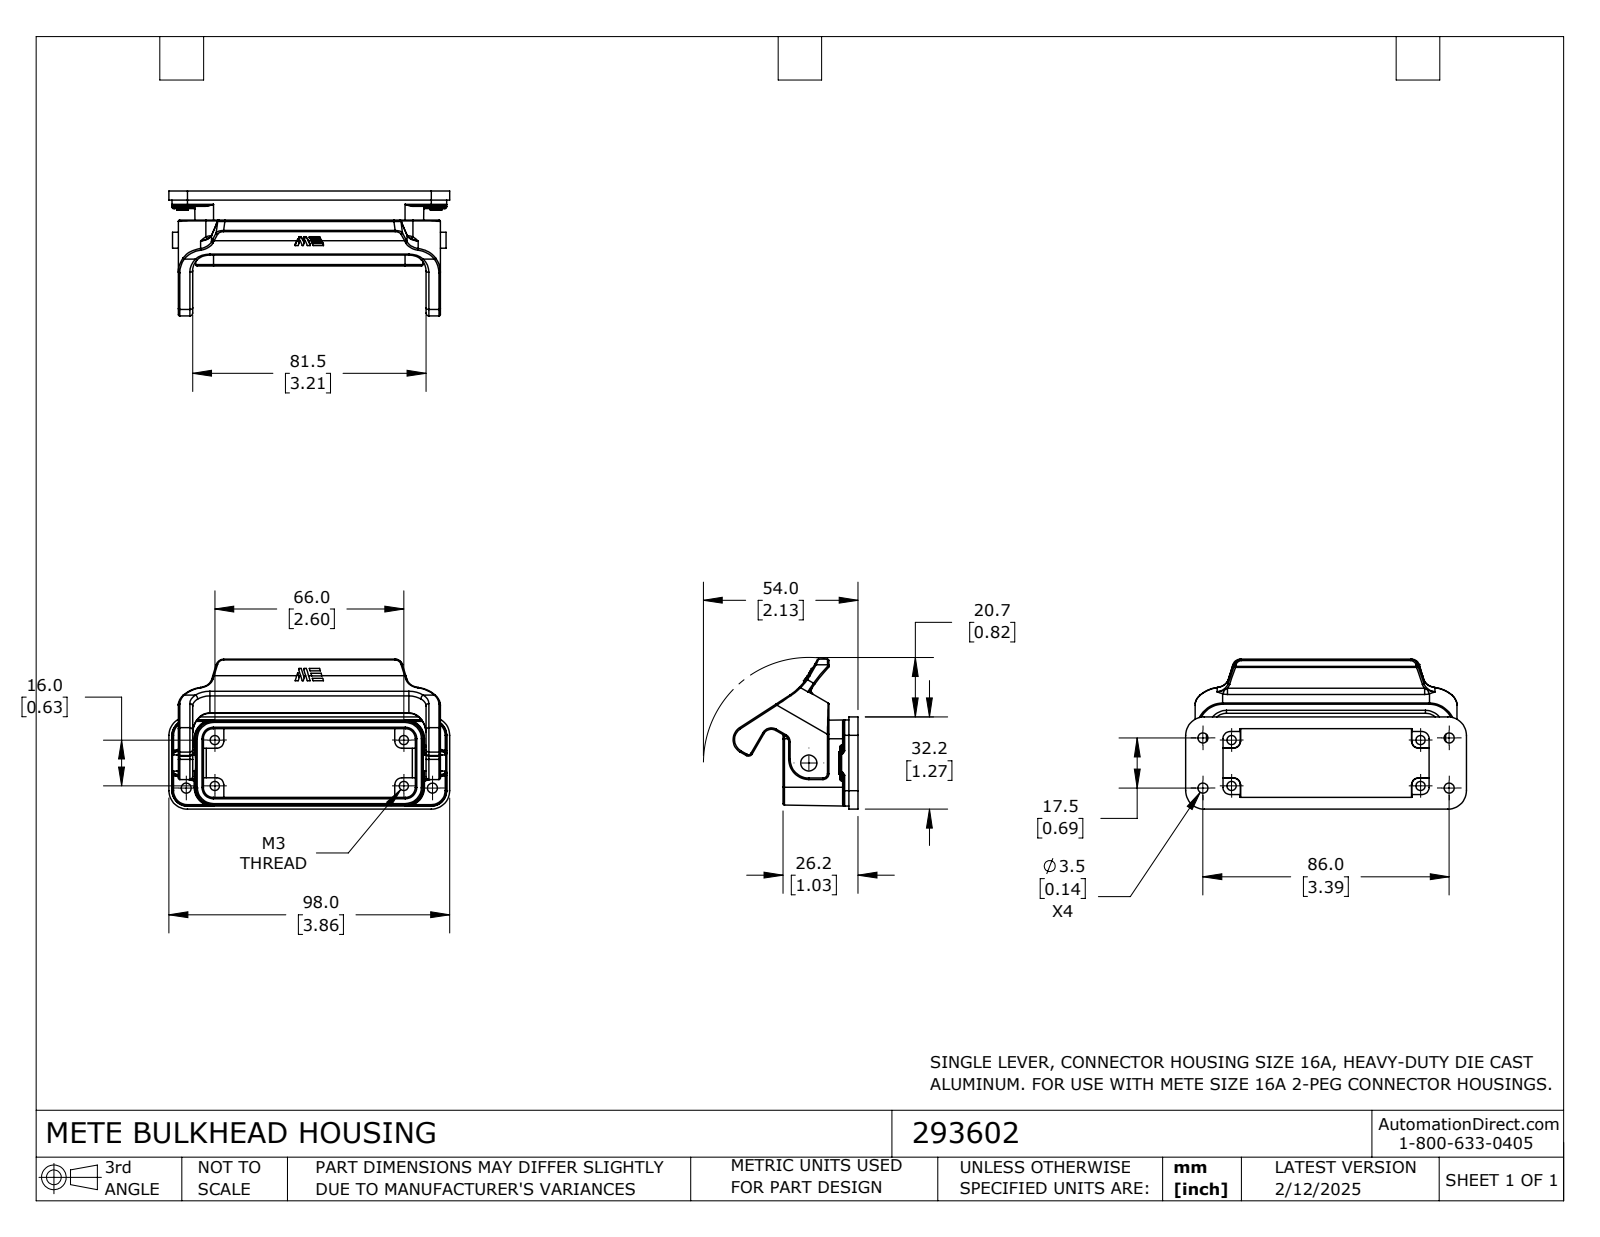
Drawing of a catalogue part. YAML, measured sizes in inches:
part_name: "293602"
step_written_by: "SolidWorks 2024 (CONFIG_CONTROL_DESIGN)"
units: inches
bodies: {solids: 1, faces: 485, planar: 174, cylindrical: 203, other: 108}
overall_size: [3.86, 2.061, 1.718]
volume: 1.99
surface_area: 33.51
round_holes:
  - {diameter: 0.126, count: 4}
  - {diameter: 0.138, count: 4}
round_bosses_or_shafts:
  - {diameter: 0.22, count: 1}
partial_cylinders:
  - {radius: 0.02, count: 40}
  - {radius: 0.004, count: 38}
  - {radius: 0.039, count: 16}
  - {radius: 0.008, count: 12}
  - {radius: 0.098, count: 11}
  - {radius: 0.138, count: 4}
  - {radius: 0.254, count: 4}
  - {radius: 0.197, count: 3}
face_to_face_distances: [0.945, 0.197, 3.061, 0.344, 3.258, 3.406, 0.148, 0.276, 0.162, 1.107]
hole_center_spacings: [0.395, 0.768, 2.992, 3.064, 0.63, 0.689, 2.598, 2.674]
